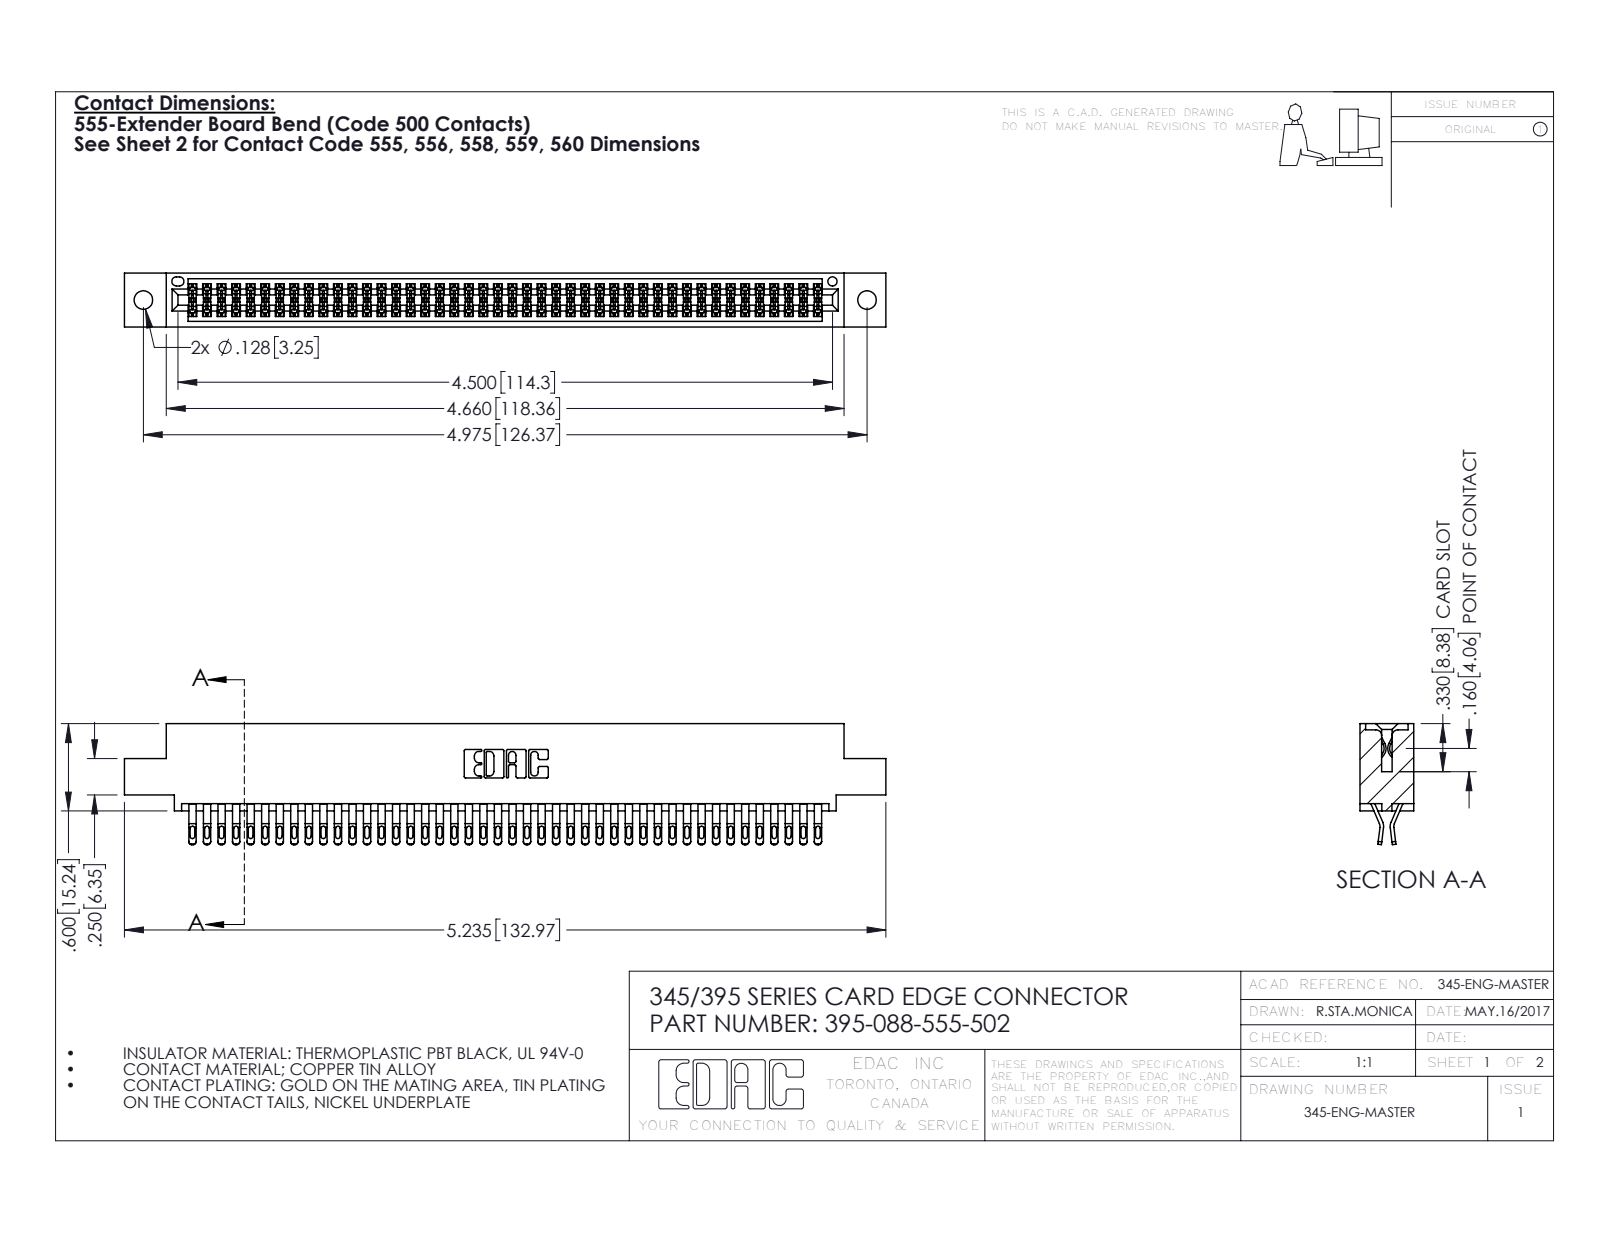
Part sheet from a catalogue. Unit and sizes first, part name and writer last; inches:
Units: inches
Overall size (bounding box): 5.235 × 0.832 × 0.37
Round holes (diameter × count): ⌀0.128 ×2, ⌀0.064 ×1
Partial cylindrical surfaces — rounded edges, fillets, slot ends (radius × count): R0.016 ×220, R0.02 ×176, R0.006 ×132, R0.01 ×22, R0.007 ×6, R0.031 ×6, R0.026 ×3, R0.01 ×2
Main face-to-face distances: 0.298, 0.072, 0.025, 0.37, 0.2, 0.098, 0.272, 0.225, 0.175, 0.149
Hole centre spacings: 0.27, 4.739, 4.975
Volume: 0.798 in³ · Surface area: 31.13 in²
Bodies: 89 solids, 5058 faces (2812 planar, 2246 cylindrical, 0 other)
Part name (STEP PRODUCT): 345 Part_0.110 Offset - 0.128 Dia; 395-088-555-502; 345-292-001_555 Tail
STEP written by: SolidWorks 2016 (CONFIG_CONTROL_DESIGN)
